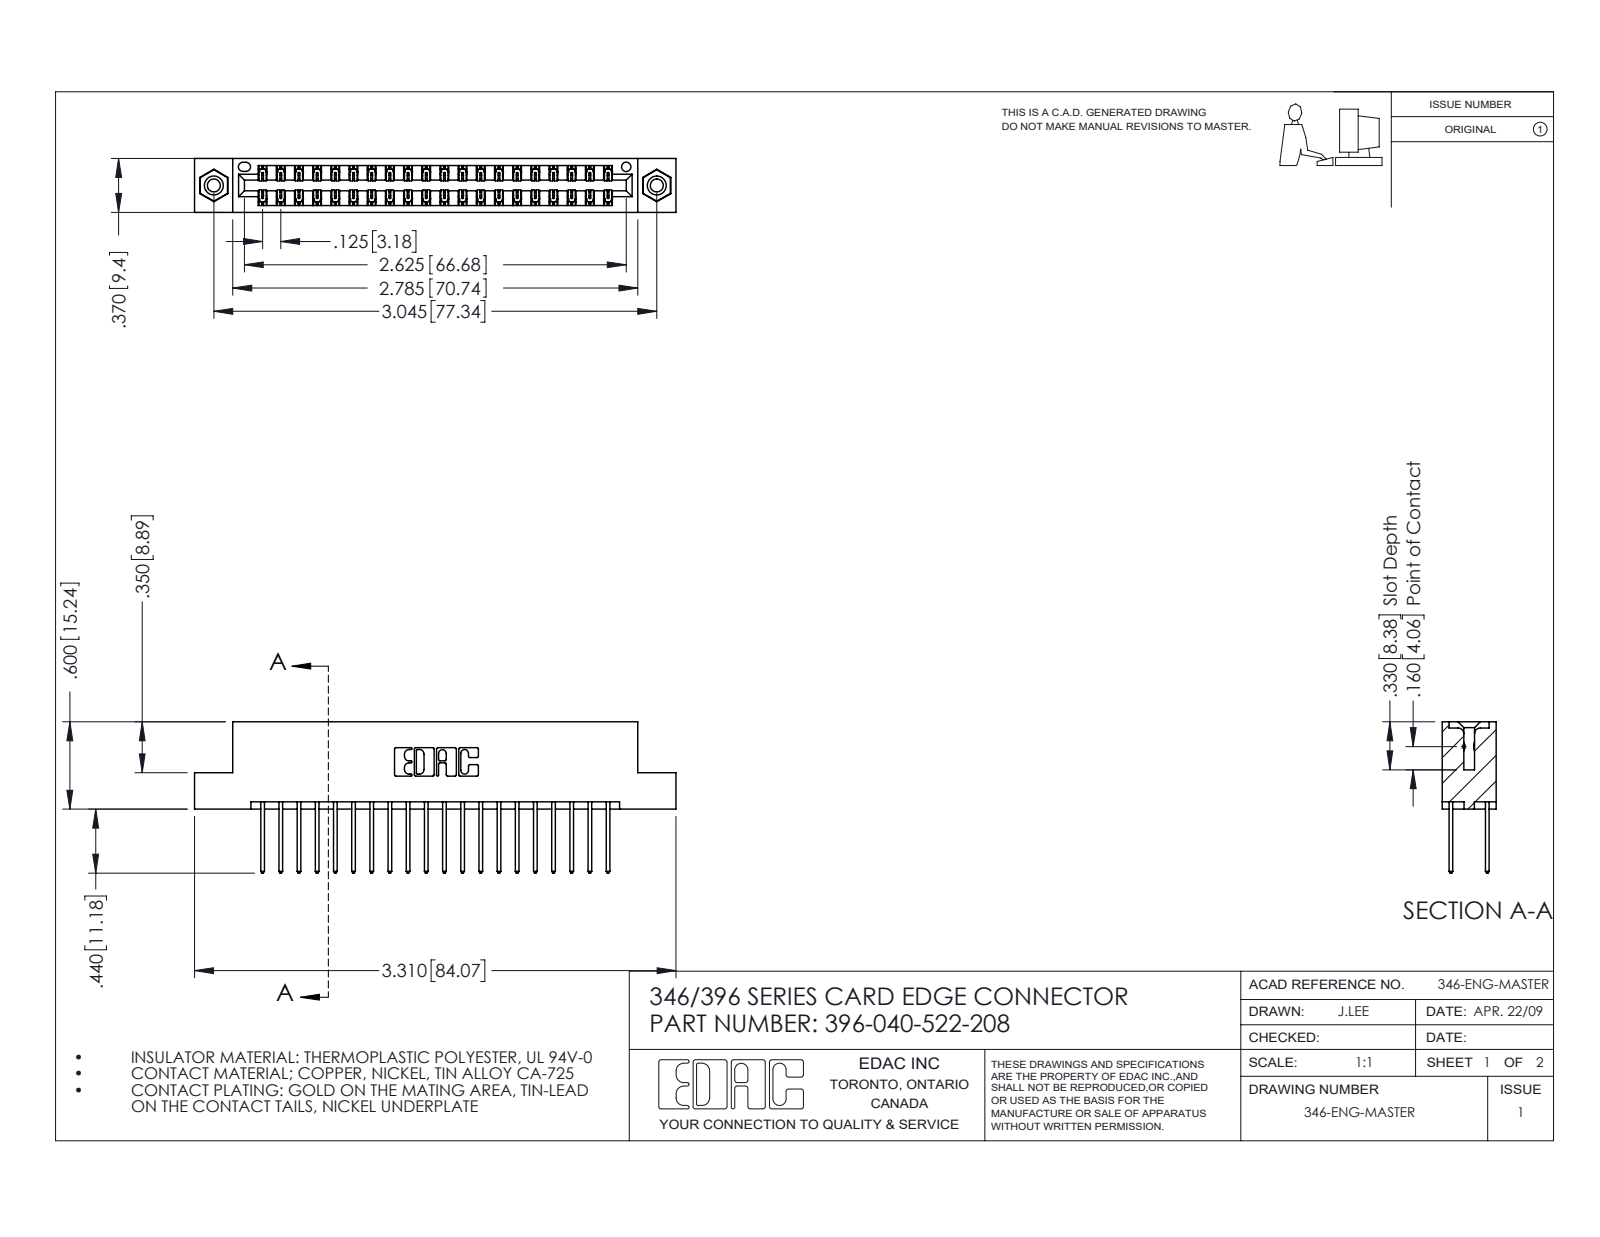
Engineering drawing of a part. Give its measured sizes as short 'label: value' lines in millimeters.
name: 346 Part_Flush Mounting Lugs - 0.156 Dia-TI; 345-292-001_345-293-122; 345-250-001_345-250-003-102; 396-040-522-208
written by: SolidWorks 2016 (CONFIG_CONTROL_DESIGN)
unit: mm
bodies: 43 solids, 2262 faces (1508 planar, 738 cylindrical, 16 other)
size: 84.1 × 26.4 × 9.4
volume: 8 130 mm³; area: 11 320 mm²
holes: 2× ⌀2.3, 2× ⌀3.2, 2× ⌀4, 1× ⌀1.6
bosses: 2× ⌀3.9
rounds: 60× R0.2, 40× R0.3, 22× R0.3, 6× R0.2, 6× R0.8, 3× R0.7, 2× R0.4, 2× R0.6
face distances: 1.2, 8.2, 6.4, 9.4, 1.8, 7.6, 0.6, 7, 3.8, 5.6
hole spacings: 6.2, 72.1, 77.3
